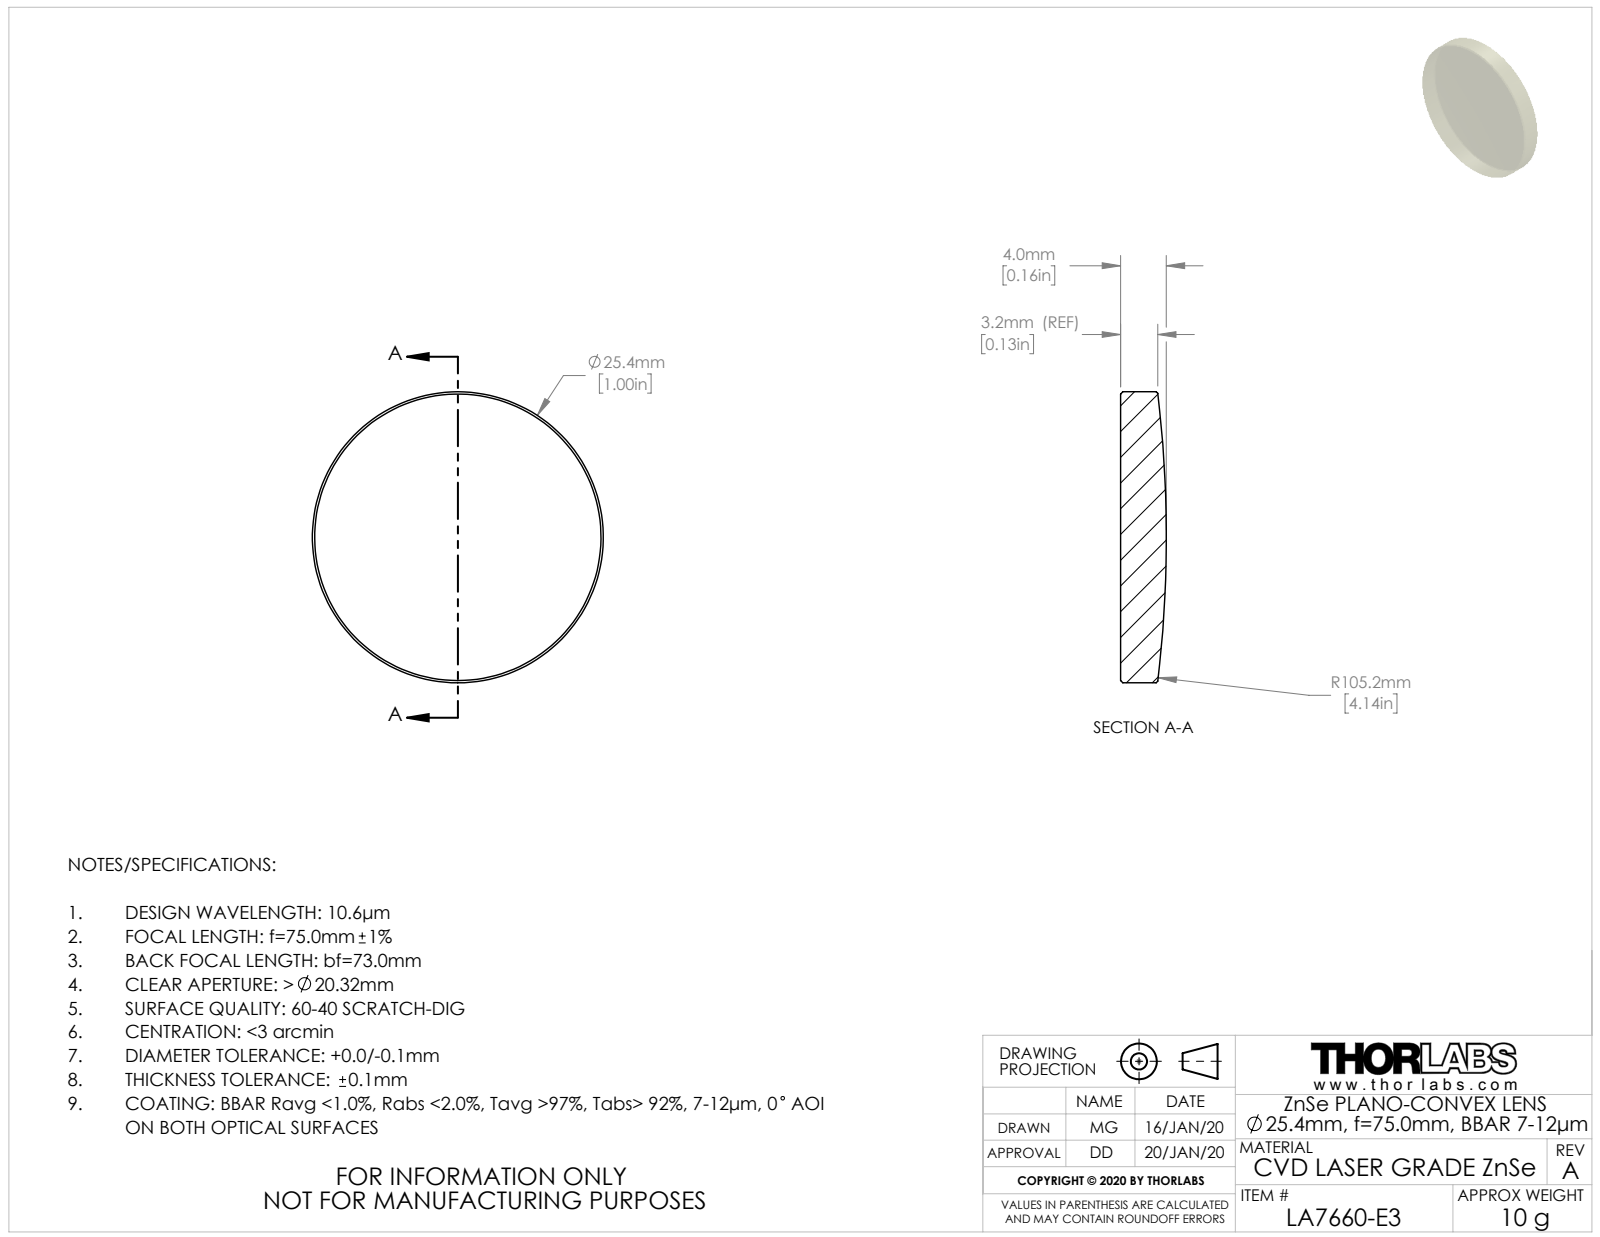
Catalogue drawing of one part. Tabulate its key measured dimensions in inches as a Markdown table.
| quantity | value |
| --- | --- |
| part name | TTN206025-E0W |
| STEP written by | SolidWorks 2018 (CONFIG_CONTROL_DESIGN) |
| units | inches |
| bodies | 1 solid, 9 faces (1 planar, 2 cylindrical, 6 other) |
| overall size | 1 × 1 × 0.157 |
| volume | 0.112 in³ |
| surface area | 1.95 in² |
| round bosses / shafts (diameter × count) | 1 × 1 |
